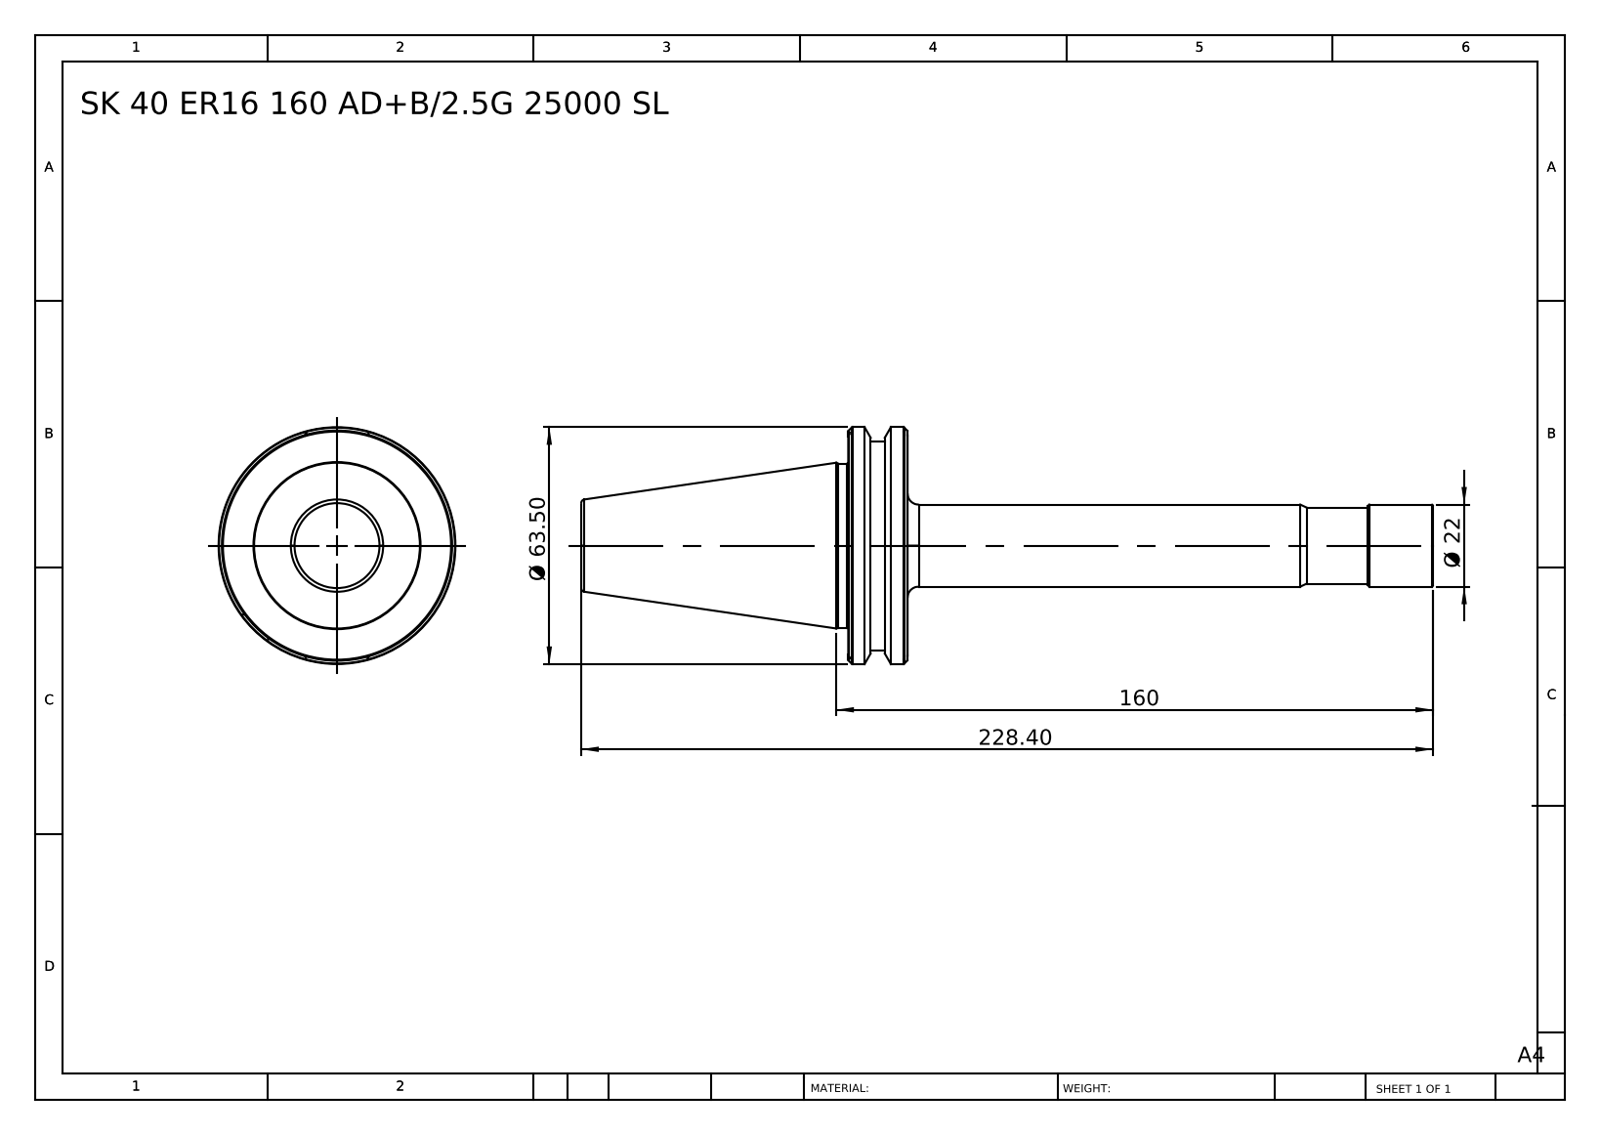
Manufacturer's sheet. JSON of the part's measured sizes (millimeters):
{"part_name": "SK40 ER16M 160 AD+B 2.5G 25000 SL", "step_written_by": "SolidWorks 2014 (CONFIG_CONTROL_DESIGN)", "units": "millimeters", "bodies": {"solids": 1, "faces": 77, "planar": 7, "cylindrical": 14, "other": 56}, "overall_size": [228.4, 63.5, 63.5], "volume_mm3": 169874, "surface_area_mm2": 26536, "round_bosses_or_shafts": [[63.5, 1], [56, 1], [44, 1], [22, 1], [20.4, 1]], "face_to_face_distances": [15.9, 87.5, 71.6, 140.9, 156.8, 228.4, 150.8, 9.9, 6, 77.6]}
